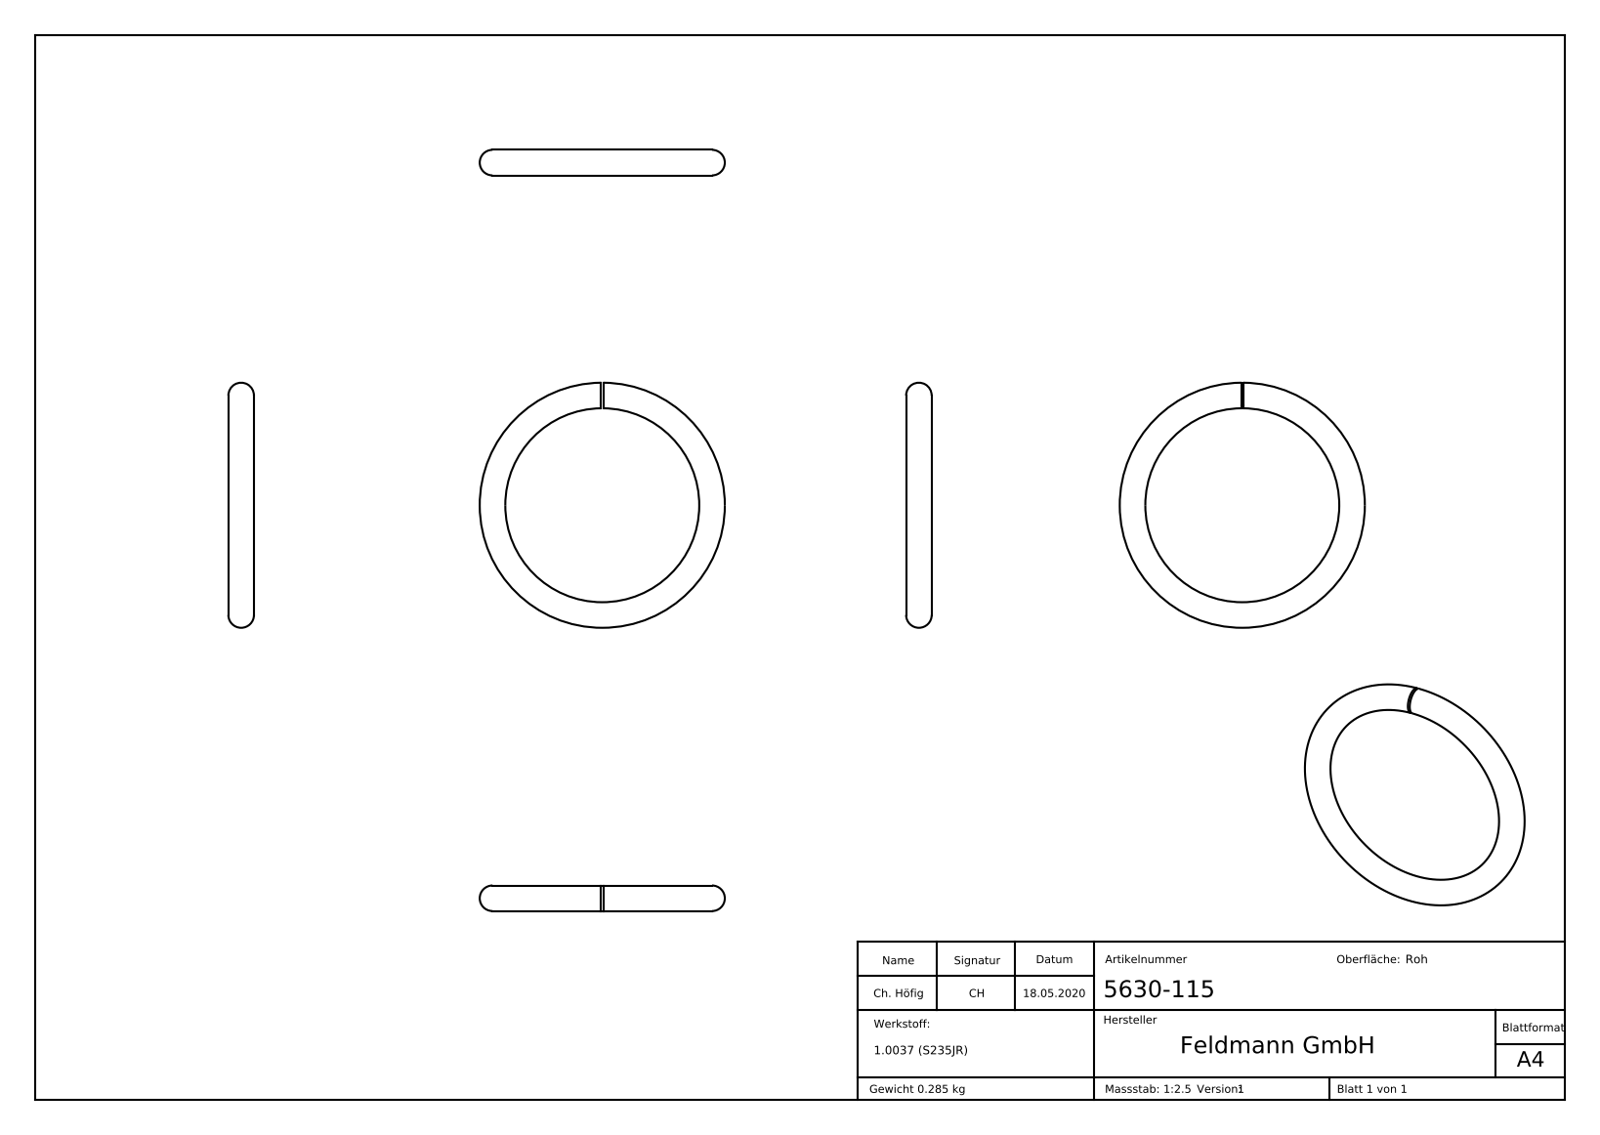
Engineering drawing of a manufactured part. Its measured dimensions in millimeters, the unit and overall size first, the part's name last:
Units: millimetres
Overall size (bounding box): 115 × 115 × 12
Main face-to-face distances: 1, 1.5, 0.5, 1.78, 0.83, 2.45, 0.99, 0.61, 2.73, 2.12
Volume: 36 488 mm³ · Surface area: 12 412 mm²
Bodies: 1 solid, 207 faces (107 planar, 0 cylindrical, 100 other)
Part name (STEP PRODUCT): 5630-115
STEP written by: SolidWorks 2015 (CONFIG_CONTROL_DESIGN)
